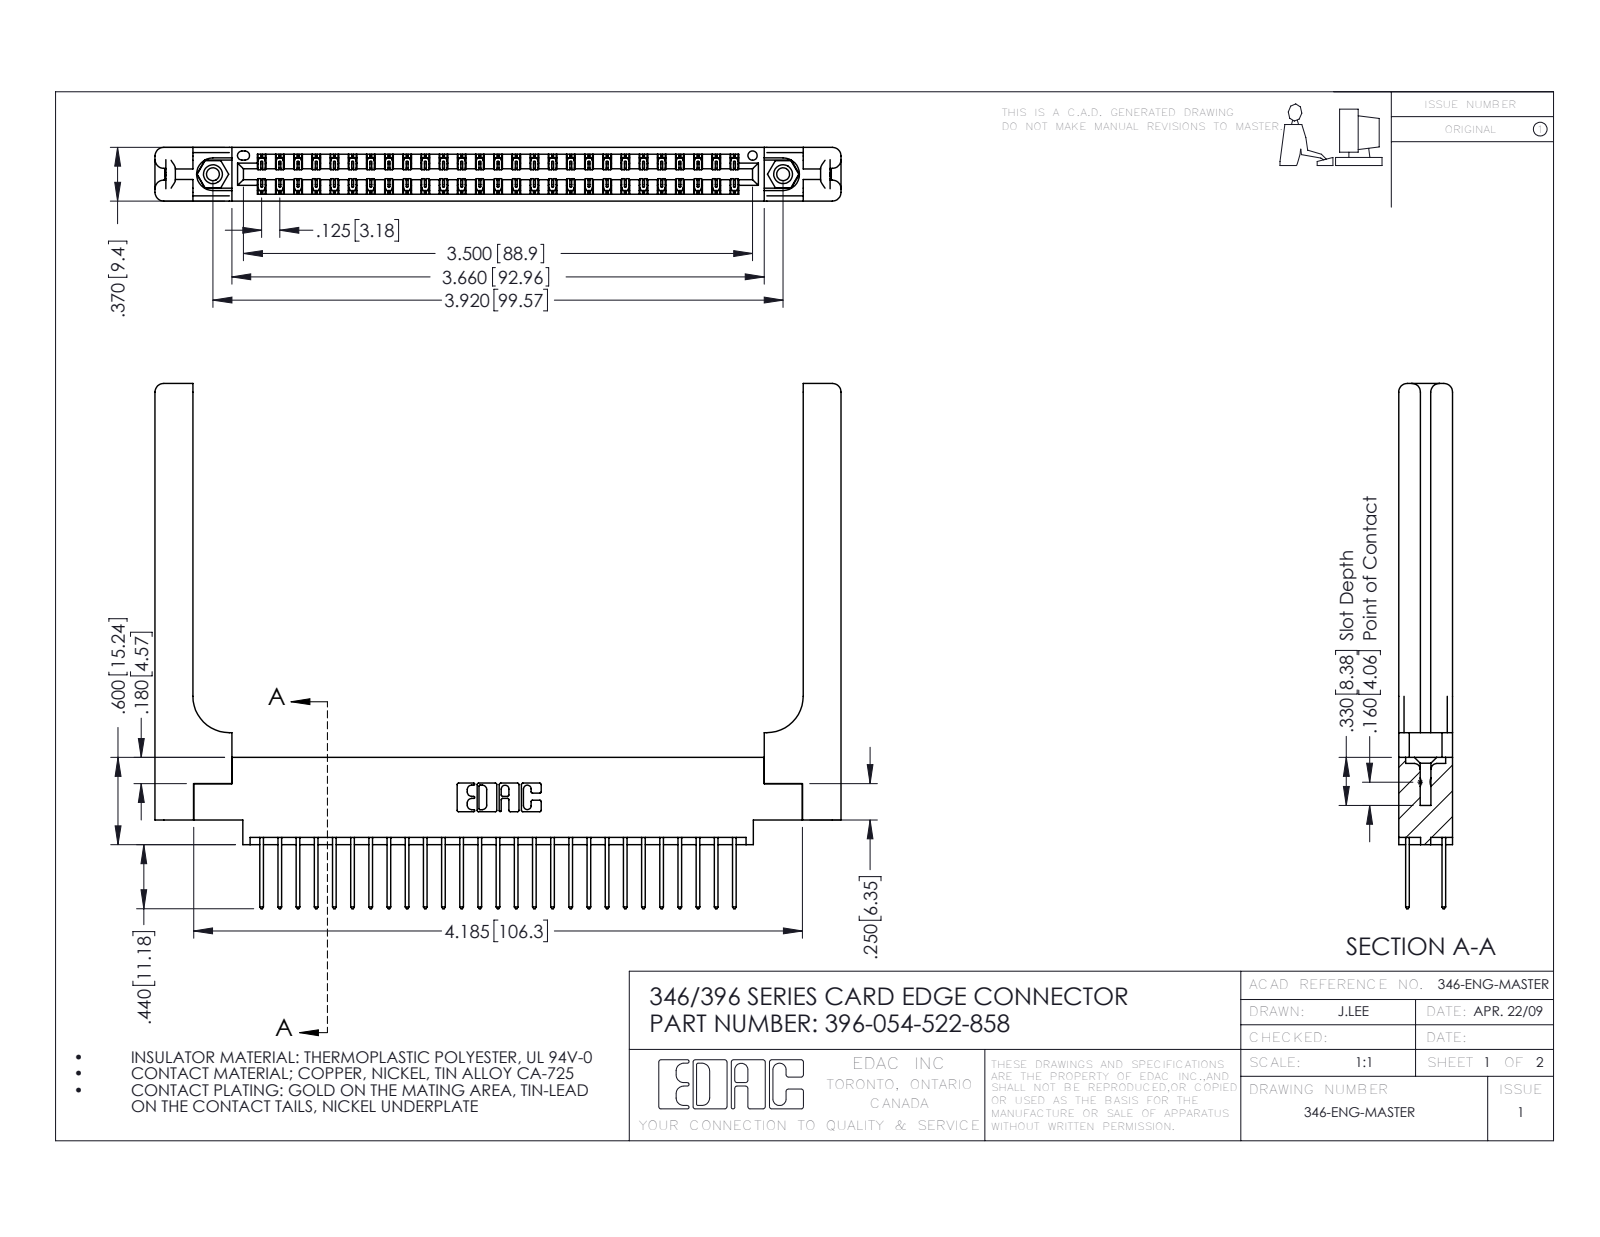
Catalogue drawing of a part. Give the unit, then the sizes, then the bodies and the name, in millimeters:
Units: millimetres
Overall size (bounding box): 119.8 × 91.7 × 9.4
Round holes (diameter × count): ⌀2.3 ×2, ⌀3.2 ×2, ⌀4 ×2, ⌀1.6 ×1
Round bosses / shafts (diameter × count): ⌀3.9 ×2
Partial cylindrical surfaces — rounded edges, fillets, slot ends (radius × count): R0.2 ×81, R0.3 ×54, R0.3 ×22, R1.5 ×16, R0.2 ×6, R0.8 ×6, R0.7 ×3, R0.4 ×2
Main face-to-face distances: 9.4, 1.8, 1.2, 8.2, 6.4, 3.8, 3.8, 0.6, 7.6, 7
Hole centre spacings: 6.2, 94.3, 99.6
Volume: 19 040 mm³ · Surface area: 21 430 mm²
Bodies: 59 solids, 3190 faces (2118 planar, 1012 cylindrical, 60 other)
Part name (STEP PRODUCT): 346 Part_0.170 Offset - 0.156 Dia-TH; 396-054-522-858; 345-250-001_345-250-001-102; 346-220-058_345-220-058 (+1 more)
STEP written by: SolidWorks 2016 (CONFIG_CONTROL_DESIGN)
